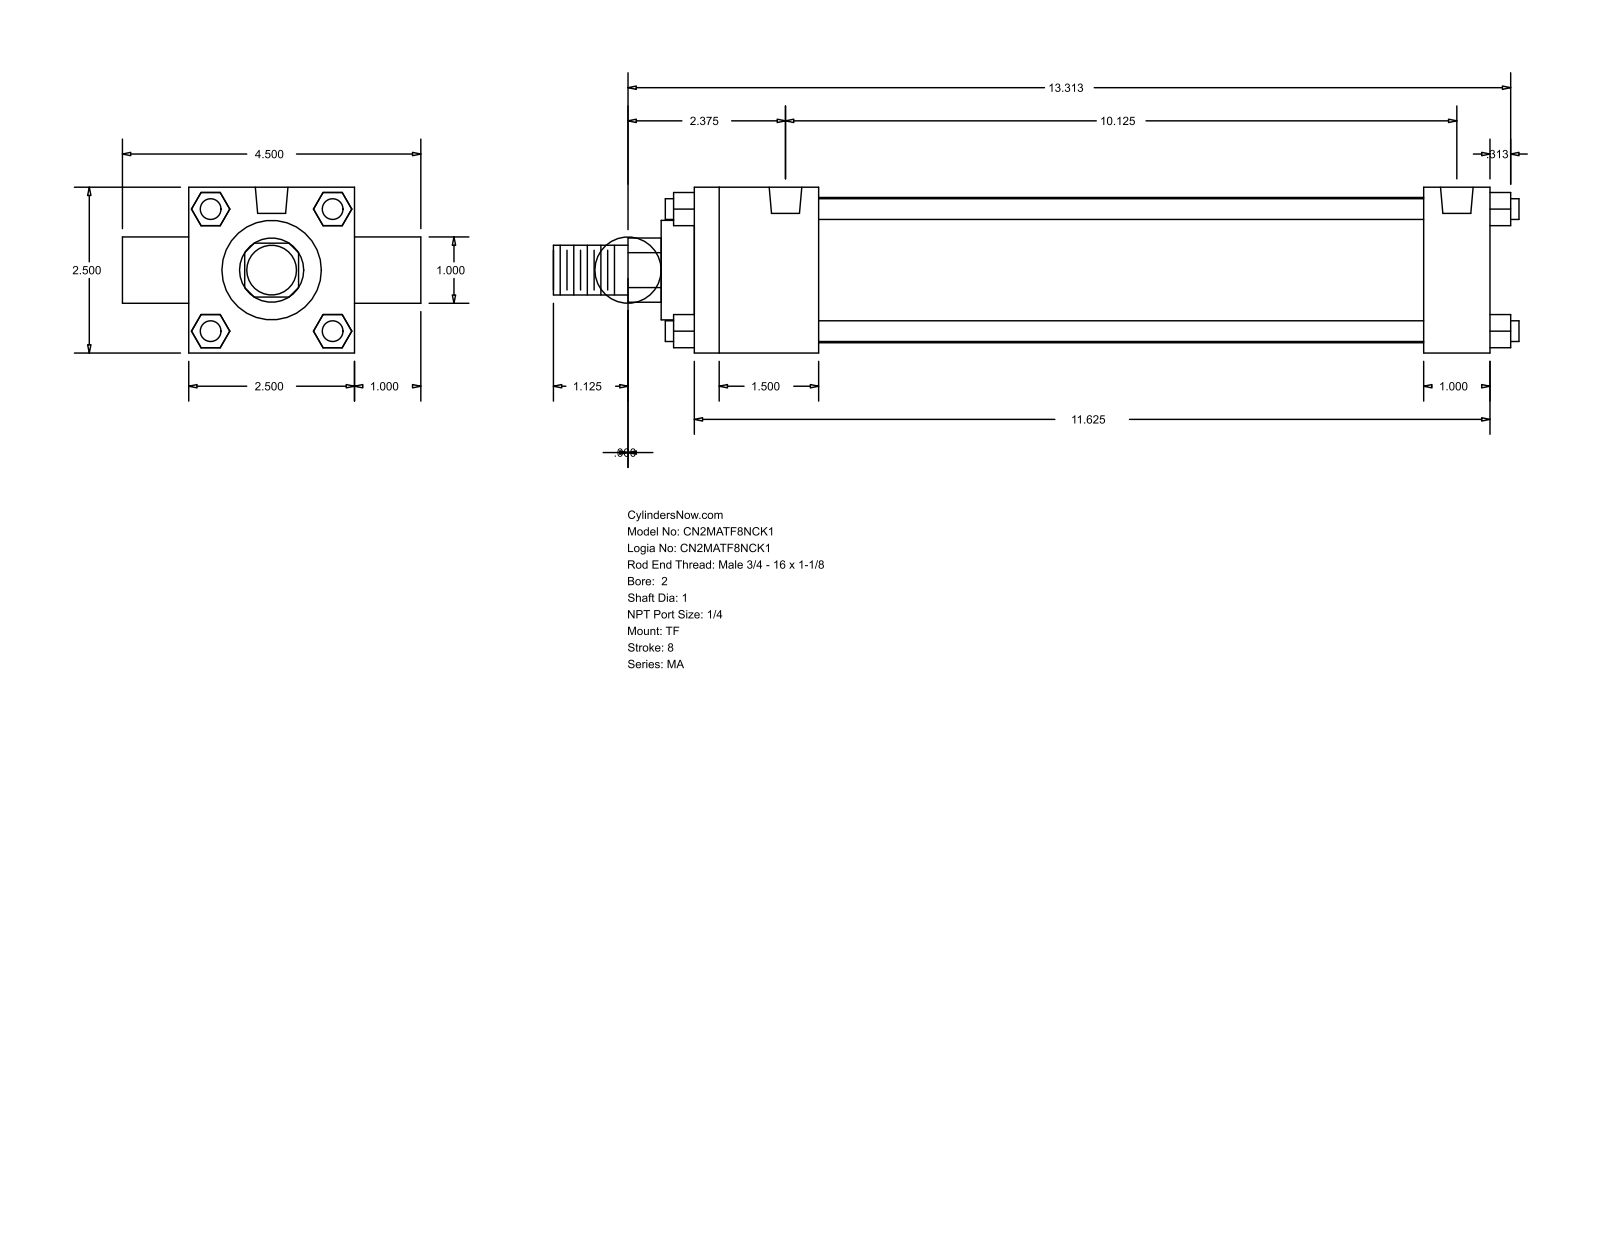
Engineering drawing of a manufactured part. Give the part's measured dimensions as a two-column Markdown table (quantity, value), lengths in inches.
| quantity | value |
| --- | --- |
| part name | MA_TF__0200_1 |
| STEP written by | GSSL Pune (CONFIG_CONTROL_DESIGN) |
| units | inches |
| bodies | 0 solids, 120 faces (92 planar, 28 cylindrical, 0 other) |
| overall size | 14.563 × 4.5 × 2.5 |
| round holes (diameter × count) | 0.313 × 3, 0.492 × 2 |
| round bosses / shafts (diameter × count) | 0.313 × 4, 1 × 2, 2.19 × 1, 1.5 × 1, 0.75 × 1 |
| partial cylindrical surfaces (radius × count) | 0.484 × 1 |
| main face-to-face distances | 2.5, 1, 12, 0.5, 1.875, 11, 9.125, 10.125, 3.5, 0.92 |
| hole center spacings | 10.125 |
